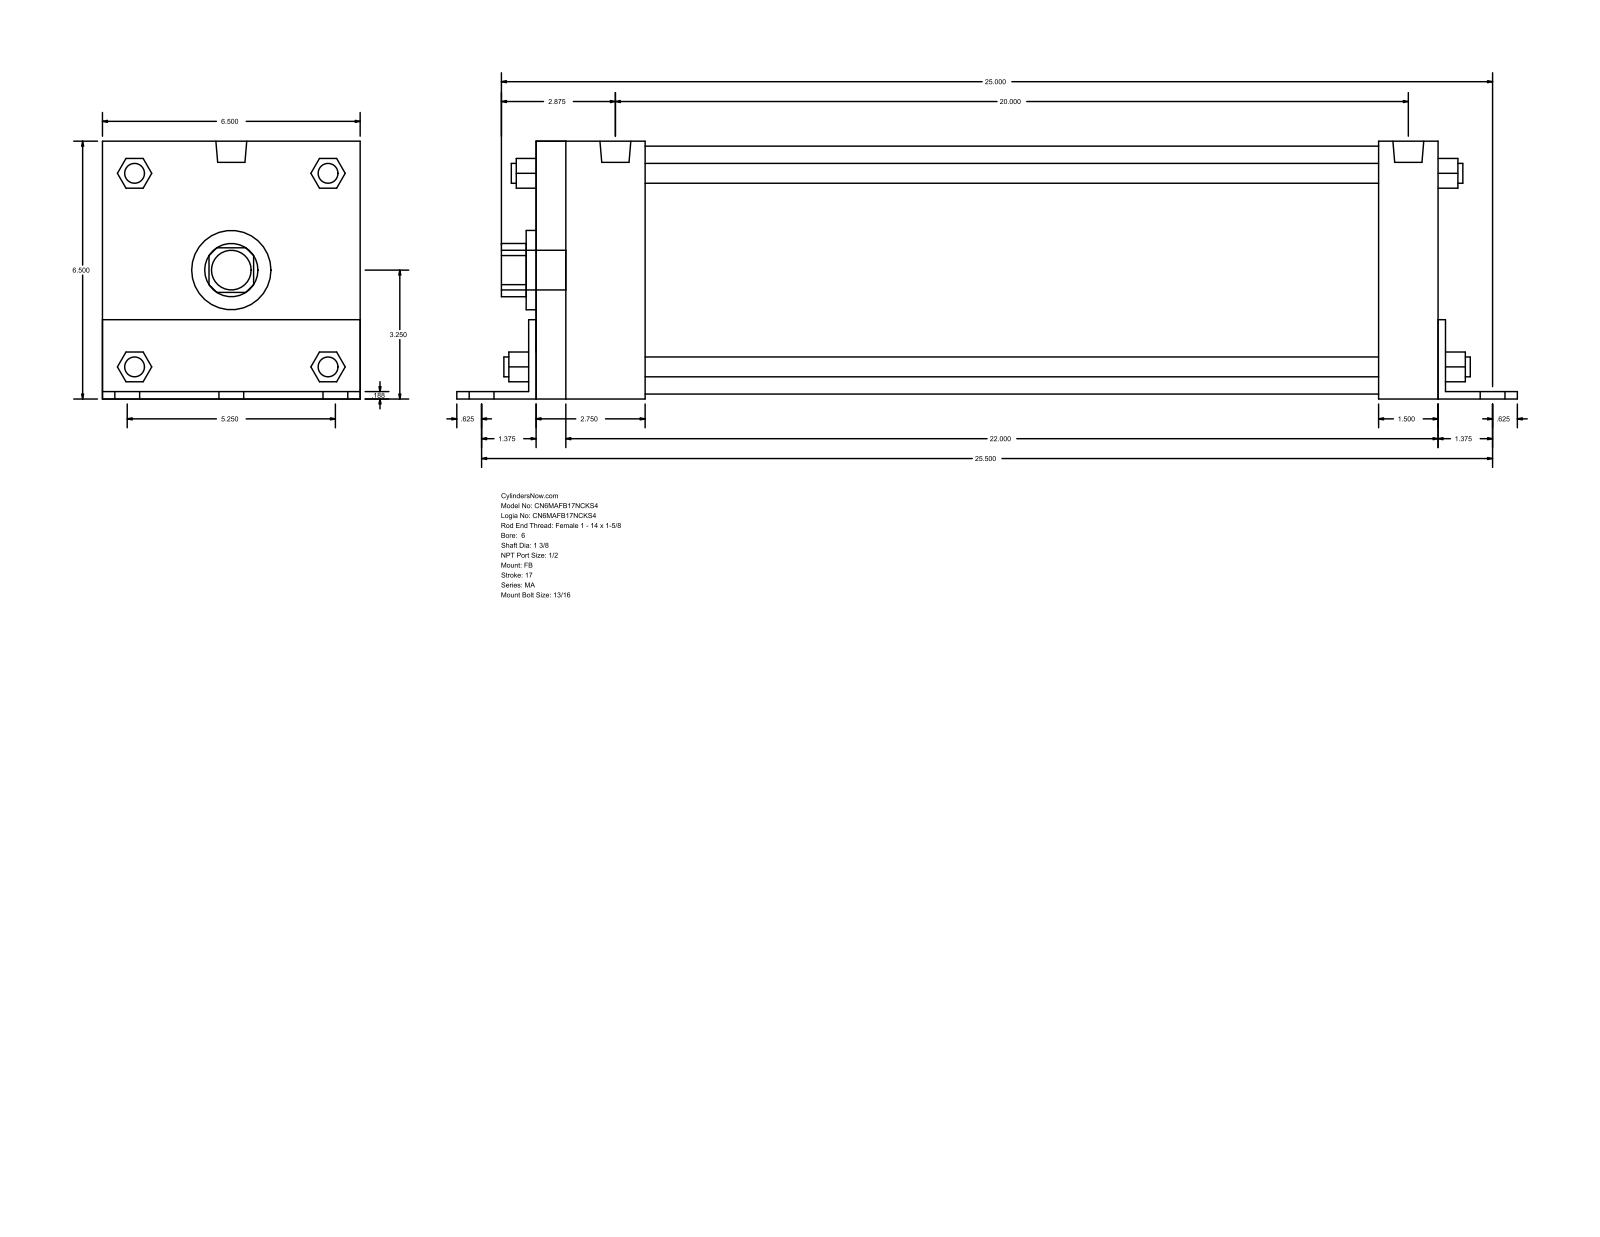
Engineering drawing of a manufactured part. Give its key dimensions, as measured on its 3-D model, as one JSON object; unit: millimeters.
{"part_name": "MA_FB__0600_1.375", "step_written_by": "GSSL Pune (CONFIG_CONTROL_DESIGN)", "units": "millimeters", "bodies": {"solids": 0, "faces": 140, "planar": 105, "cylindrical": 35, "other": 0}, "overall_size": [676.27, 165.15, 165.1], "round_holes": [[34.92, 1], [50.8, 1], [158.75, 1]], "round_bosses_or_shafts": [[20.64, 6], [17.46, 4], [12.7, 4], [19.77, 2], [25.4, 1]], "partial_cylinders_radius": [[17.06, 1], [32.05, 1]], "face_to_face_distances": [165.1, 4.76, 574.67, 165.15, 4.71, 160.39, 4.77, 38.1, 579.44, 584.2]}
